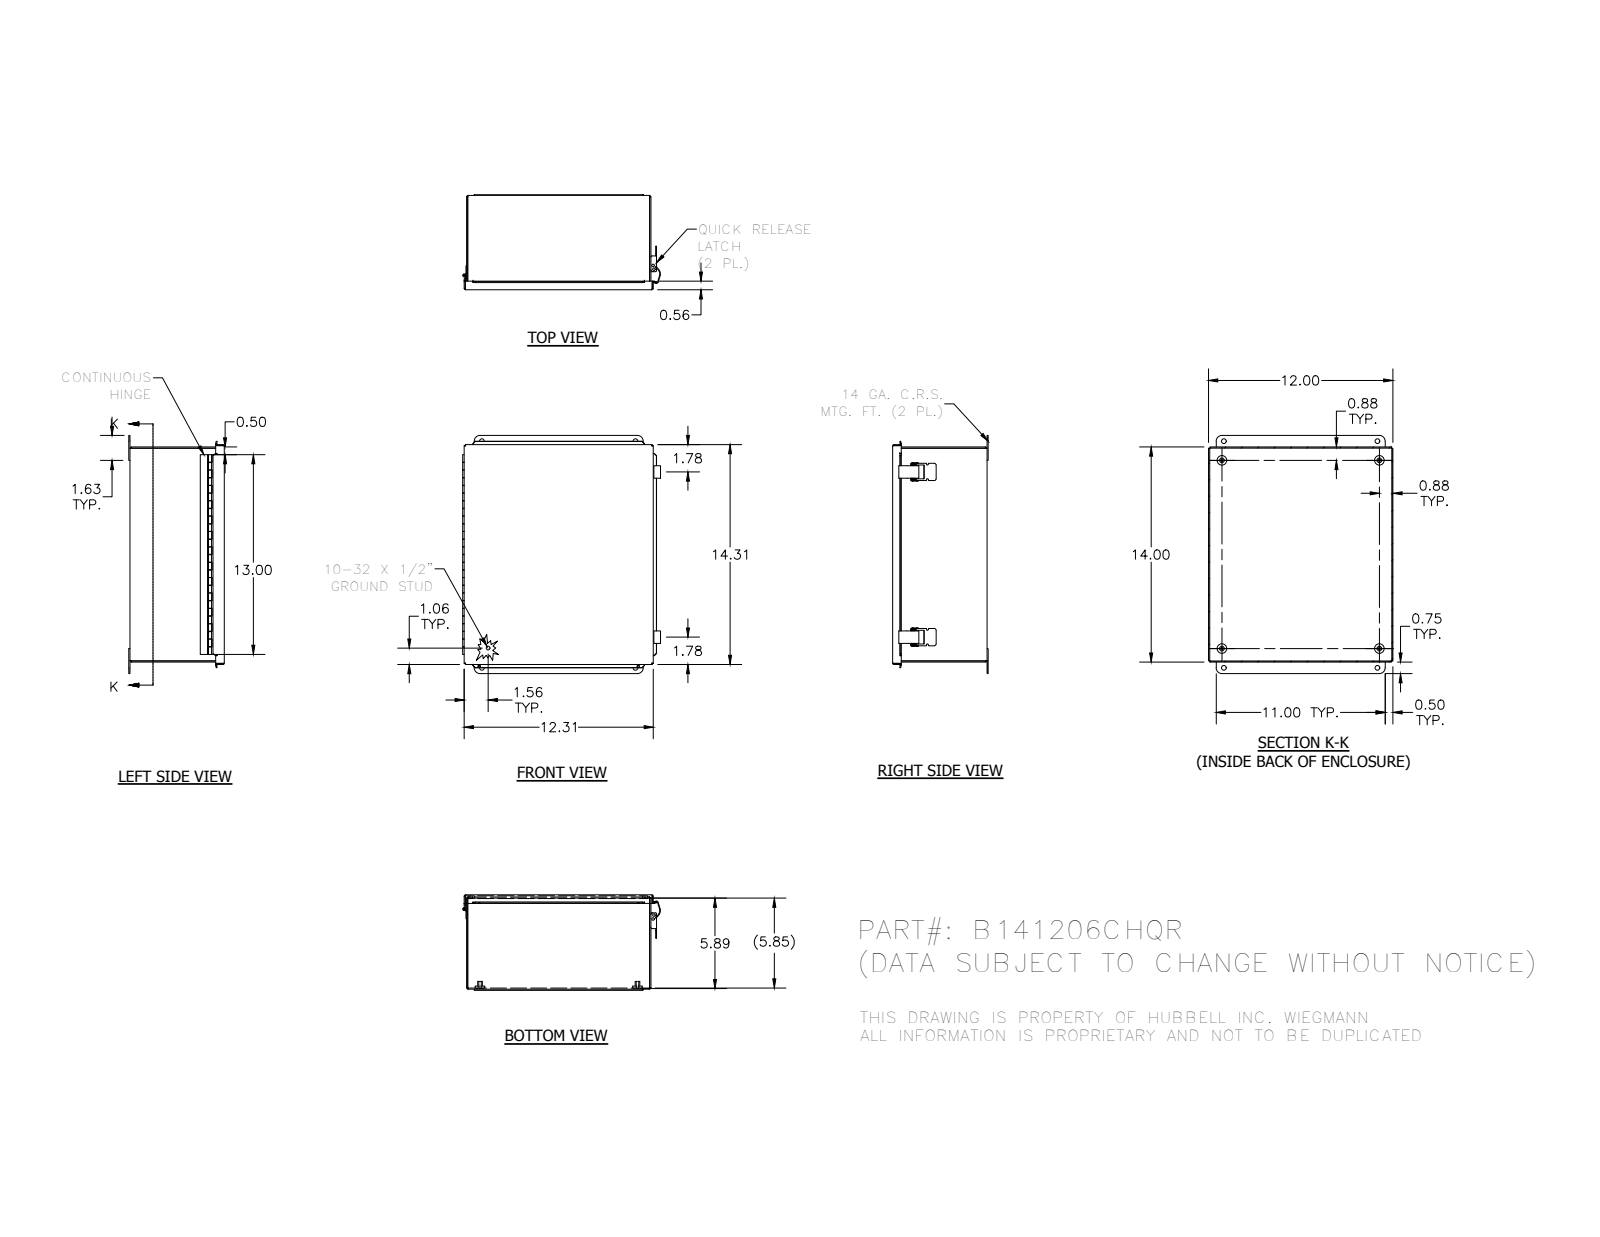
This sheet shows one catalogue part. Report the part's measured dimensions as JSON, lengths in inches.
{"part_name": "B141206CHQR; 3499; 3485; B141206CHQRBKP (+8 more)", "step_written_by": "Autodesk Inventor 2012 (AUTOMOTIVE_DESIGN)", "units": "inches", "bodies": {"solids": 24, "faces": 609, "planar": 375, "cylindrical": 187, "other": 47}, "overall_size": [15.5, 12.88, 6.219], "volume_in3": 59.22, "surface_area_in2": 1638, "round_holes": [[0.156, 4], [0.31, 4], [0.14, 2], [0.155, 2], [0.116, 1], [0.17, 1]], "round_bosses_or_shafts": [[0.625, 4], [0.3, 4], [0.25, 2], [0.169, 2], [0.136, 2], [0.2, 1], [0.19, 1], [0.1, 1]], "partial_cylinders_radius": [[0.031, 20], [0.105, 8], [0.093, 7], [0.063, 5], [0.109, 4], [0.375, 4], [0.125, 2], [0.062, 1]], "face_to_face_distances": [0.074, 6.083, 0.062, 6.144, 6.009, 6.07, 11.926, 13.926, 12, 11.852], "hole_center_spacings": [10.202, 1.256, 10, 10.25, 13.5, 14.75, 15.973, 16.875]}
